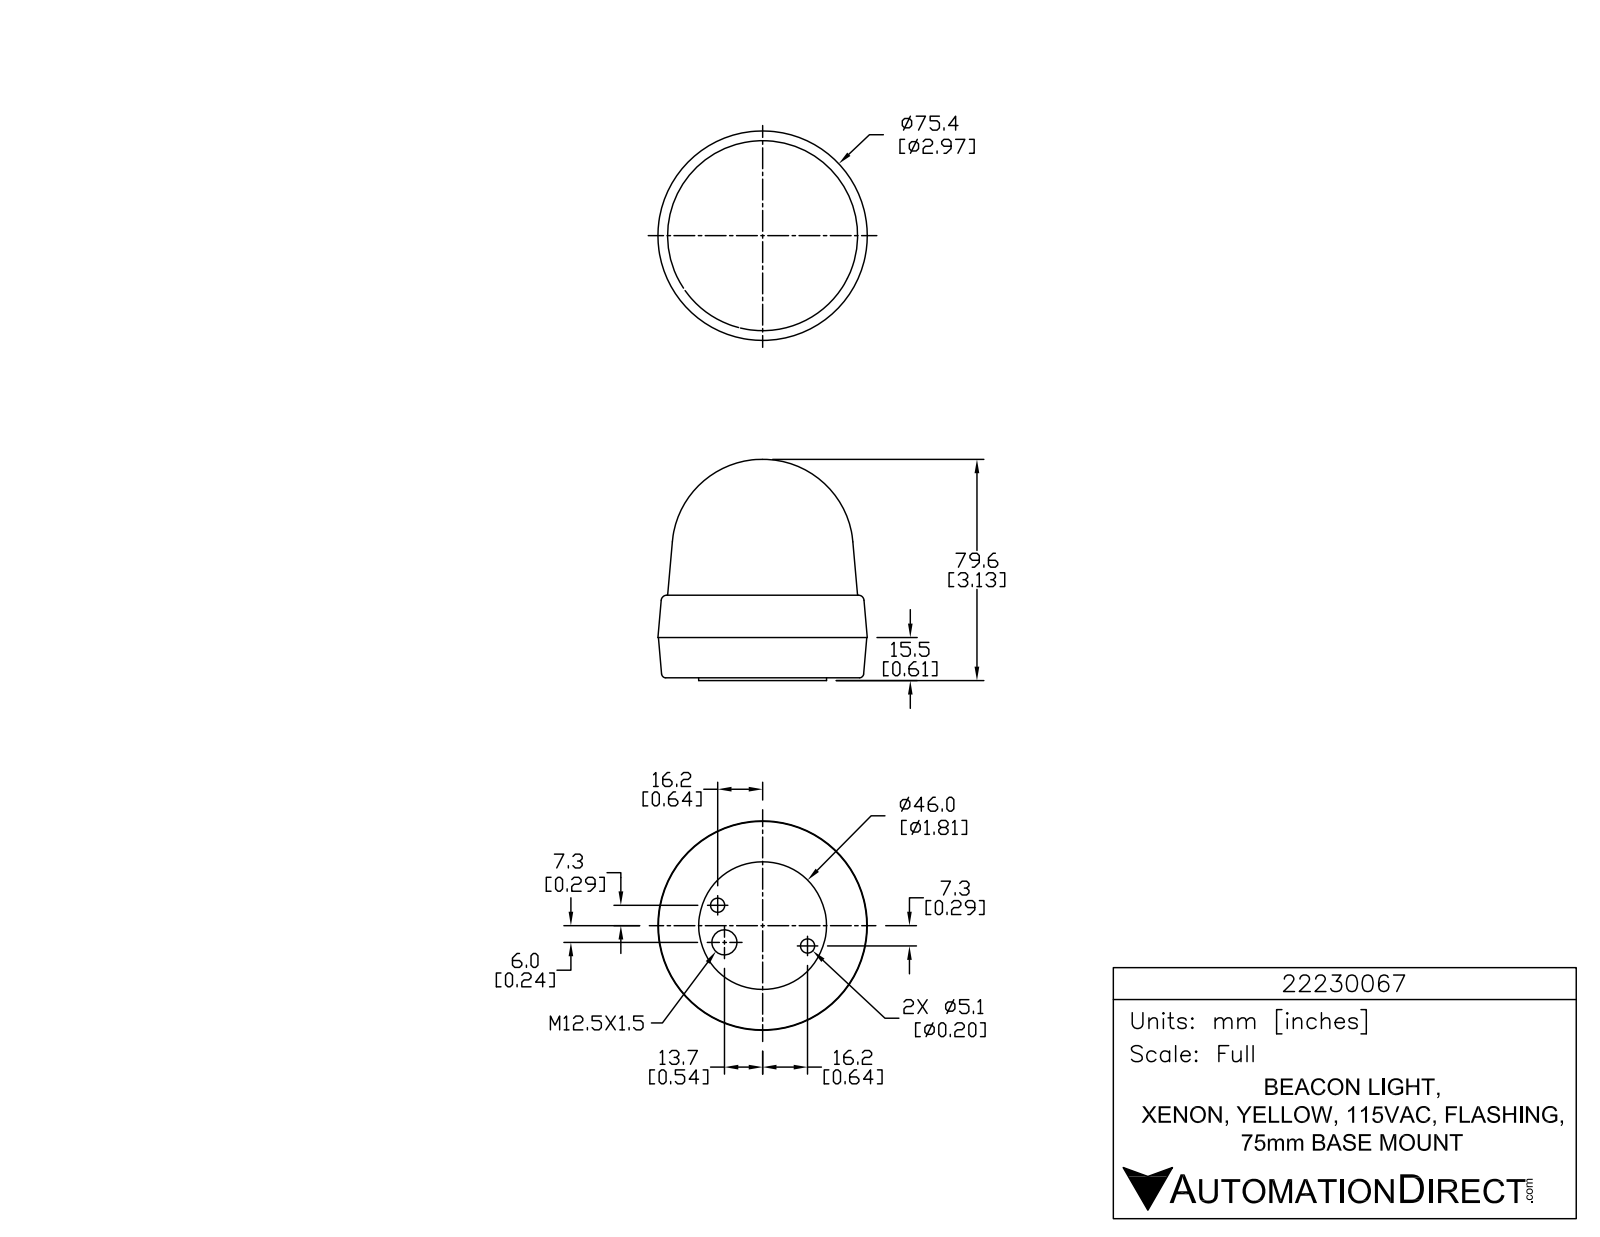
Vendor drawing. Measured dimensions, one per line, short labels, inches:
name: 22230067
written by: SolidWorks 2015 (AUTOMOTIVE_DESIGN)
unit: in
bodies: 1 solid, 773 faces (526 planar, 163 cylindrical, 84 other)
size: 3.133 × 2.967 × 2.967
volume: 15.79 in³; area: 33.7 in²
holes: 3× ⌀0.059, 2× ⌀0.201, 1× ⌀0.354
bosses: 3× ⌀0.339, 3× ⌀0.084, 1× ⌀1.811
rounds: 9× R0.005, 6× R0.005, 6× R0.012, 6× R0.012, 6× R0.012, 6× R0.196, 3× R0.005, 3× R0.005
face distances: 0.039, 1.209, 1.17, 0.61, 0.571, 0.599, 1.566, 1.527, 0.956, 0.357
hole spacings: 0.534, 1.179, 1.398
